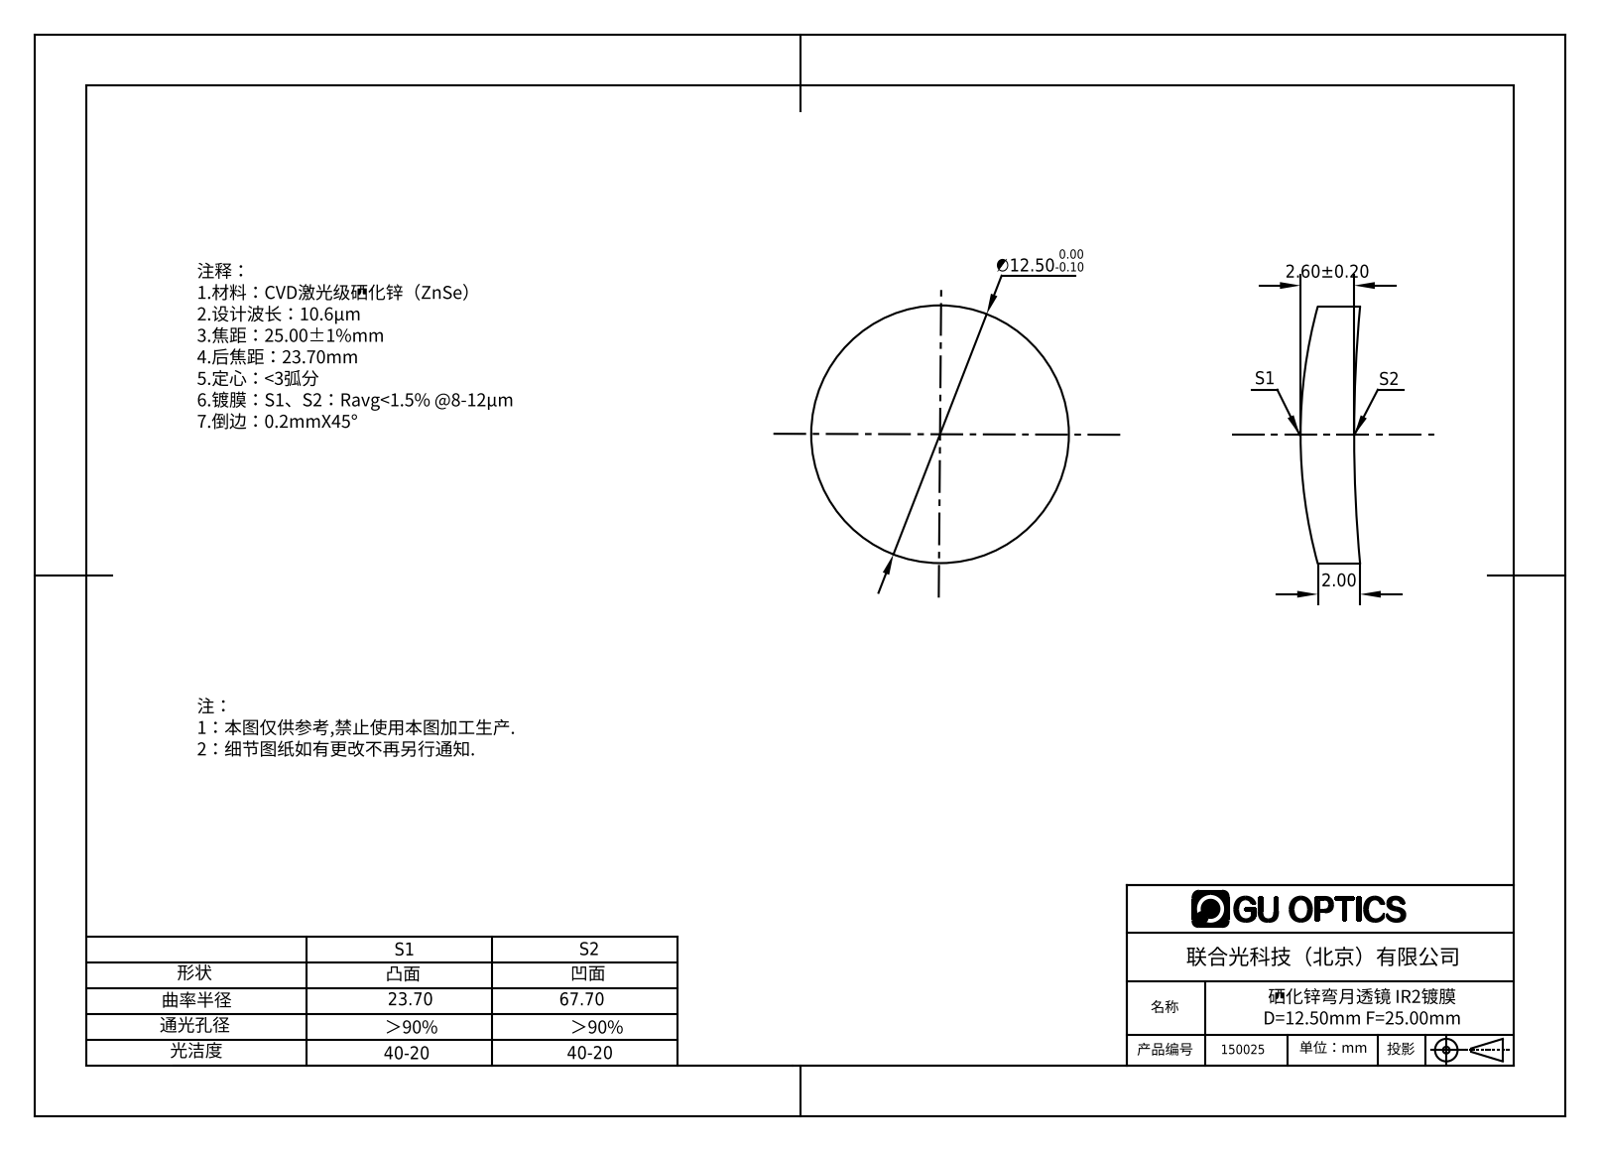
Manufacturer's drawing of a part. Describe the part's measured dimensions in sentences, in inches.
The part is named "150000". Its 3-D file was written by "SolidWorks 2016 (AUTOMOTIVE_DESIGN)". It is 1 solid with 6 faces: 0 planar, 2 cylindrical and 4 other. Overall it measures 0.492 by 0.492 by 0.114 inches. Its volume is 0.017 cubic inches and its surface area 0.508 square inches. Round bosses or shafts: 1 of diameter 0.492.
